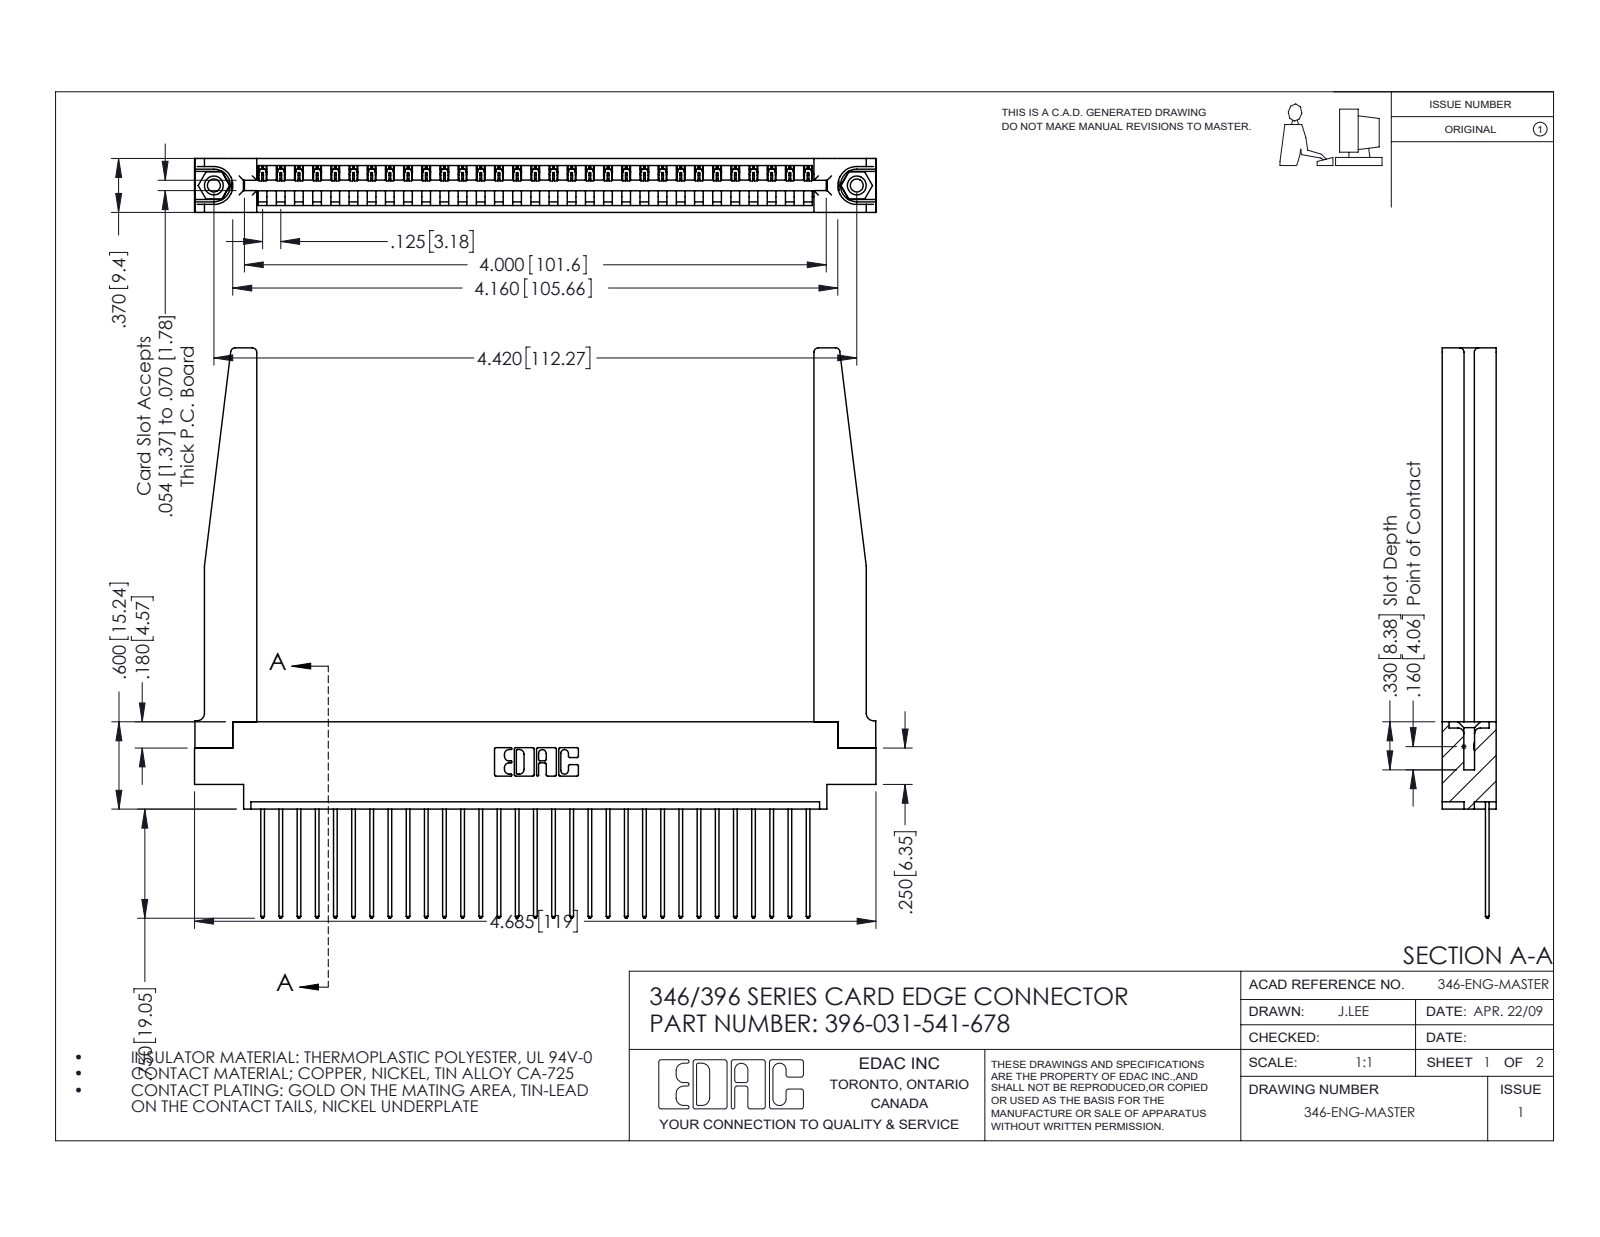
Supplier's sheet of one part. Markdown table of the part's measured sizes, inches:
| quantity | value |
| --- | --- |
| part name | 346-220-078_345-220-078; 345-250-001_345-250-001-102; 345-292-001_345-293-141; 346 Part_0.170 Offset - 0.156 Dia-TH (+1 more) |
| STEP written by | SolidWorks 2016 (CONFIG_CONTROL_DESIGN) |
| units | inches |
| bodies | 36 solids, 2158 faces (1462 planar, 644 cylindrical, 52 other) |
| overall size | 4.685 × 3.92 × 0.37 |
| volume | 1.109 in³ |
| surface area | 32.97 in² |
| round holes (diameter × count) | 0.089 × 2, 0.125 × 2, 0.156 × 2, 0.064 × 1 |
| round bosses / shafts (diameter × count) | 0.155 × 2 |
| partial cylindrical surfaces (radius × count) | 0.006 × 62, 0.01 × 62, 0.01 × 22, 0.03 × 8, 0.007 × 6, 0.031 × 6, 0.026 × 3, 0.031 × 2 |
| main face-to-face distances | 0.37, 0.048, 0.322, 0.072, 0.148, 0.15, 0.25, 0.298, 0.025, 0.222 |
| hole center spacings | 0.246, 4.212, 4.42 |
